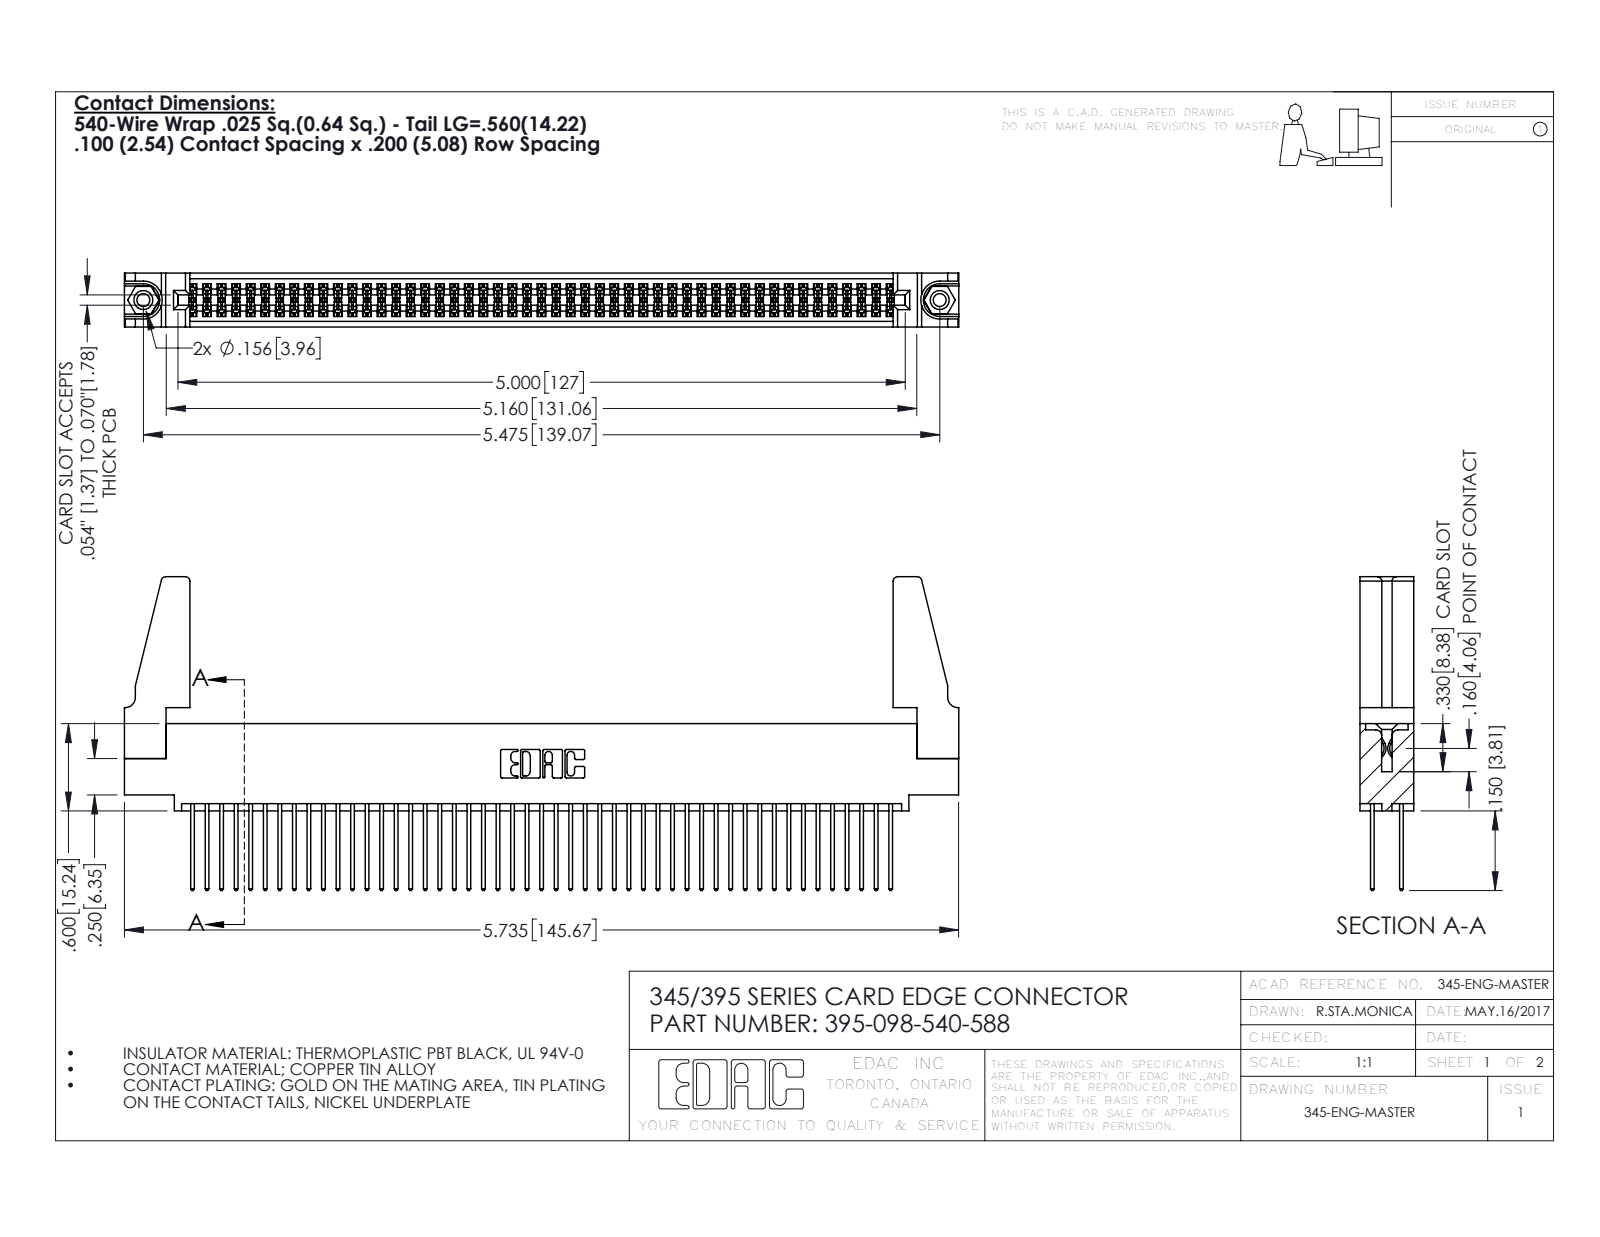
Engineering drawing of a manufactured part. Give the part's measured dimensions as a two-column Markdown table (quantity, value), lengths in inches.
| quantity | value |
| --- | --- |
| part name | 345-220-078_345-220-088; 345 Part_0.110 Offset - 0.156 Dia-TH; 395-098-540-588; 345-292-001_345-293-140 (+1 more) |
| STEP written by | SolidWorks 2016 (CONFIG_CONTROL_DESIGN) |
| units | inches |
| bodies | 103 solids, 5154 faces (3390 planar, 1748 cylindrical, 16 other) |
| overall size | 5.736 × 2.157 × 0.37 |
| volume | 1.084 in³ |
| surface area | 41.12 in² |
| round holes (diameter × count) | 0.089 × 2, 0.125 × 2, 0.156 × 2, 0.064 × 1 |
| round bosses / shafts (diameter × count) | 0.155 × 2 |
| partial cylindrical surfaces (radius × count) | 0.006 × 147, 0.01 × 98, 0.01 × 22, 0.03 × 8, 0.007 × 6, 0.031 × 6, 0.026 × 3, 0.014 × 2 |
| main face-to-face distances | 0.072, 0.298, 0.2, 0.098, 0.272, 0.025, 0.37, 0.225, 0.175, 0.149 |
| hole center spacings | 0.27, 5.239, 5.475 |
